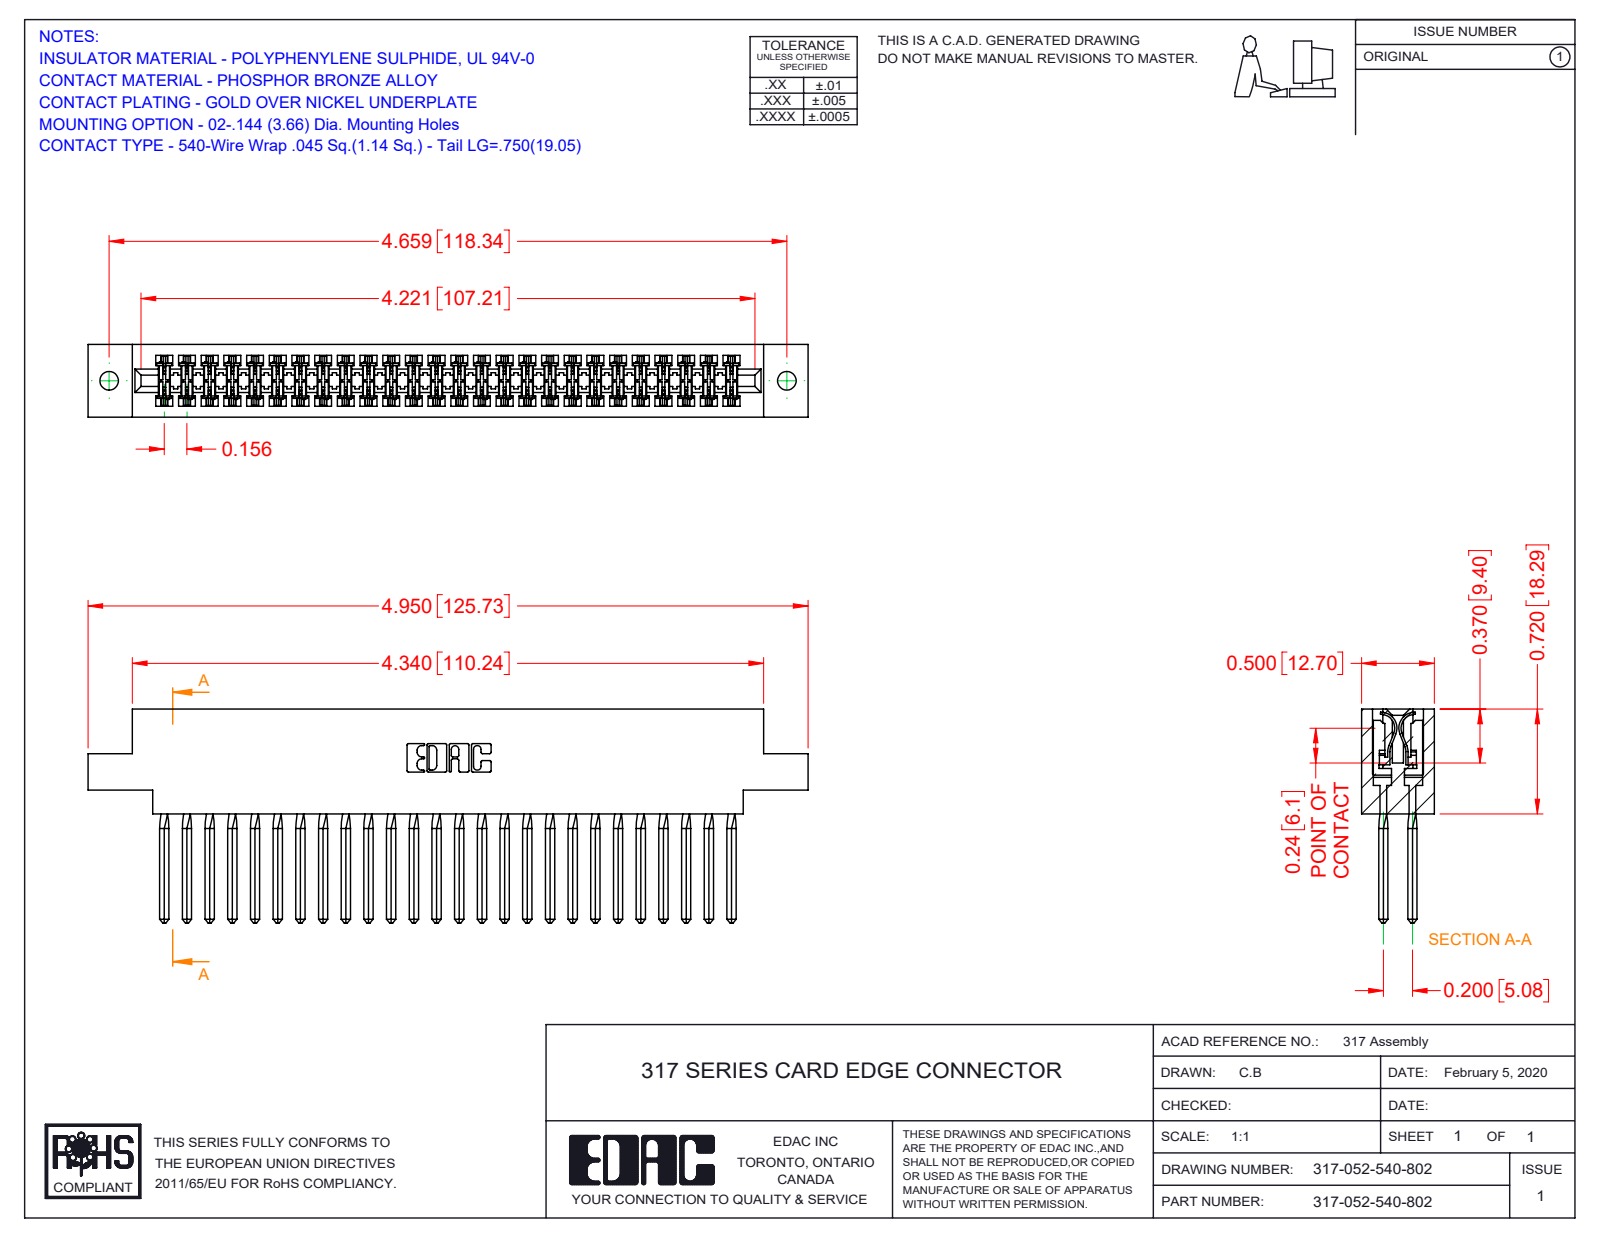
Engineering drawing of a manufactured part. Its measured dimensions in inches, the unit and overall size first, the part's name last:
Units: inches
Overall size (bounding box): 4.95 × 1.47 × 0.5
Round holes (diameter × count): ⌀0.128 ×2
Partial cylindrical surfaces — rounded edges, fillets, slot ends (radius × count): R0.015 ×104, R0.01 ×22, R0.007 ×6, R0.031 ×6, R0.026 ×3, R0.095 ×2, R0.1 ×2, R0.11 ×2
Main face-to-face distances: 0.5, 0.075, 0.425, 0.35, 0.11, 0.195, 0.094, 0.72, 0.2, 0.115
Hole centre spacings: 4.659
Volume: 1.252 in³ · Surface area: 46.08 in²
Bodies: 53 solids, 4730 faces (3854 planar, 668 cylindrical, 208 other)
Part name (STEP PRODUCT): 317-290-001_540; 317-052-540-802; 317 Part_.144 Dia
STEP written by: SolidWorks 2016 (CONFIG_CONTROL_DESIGN)
